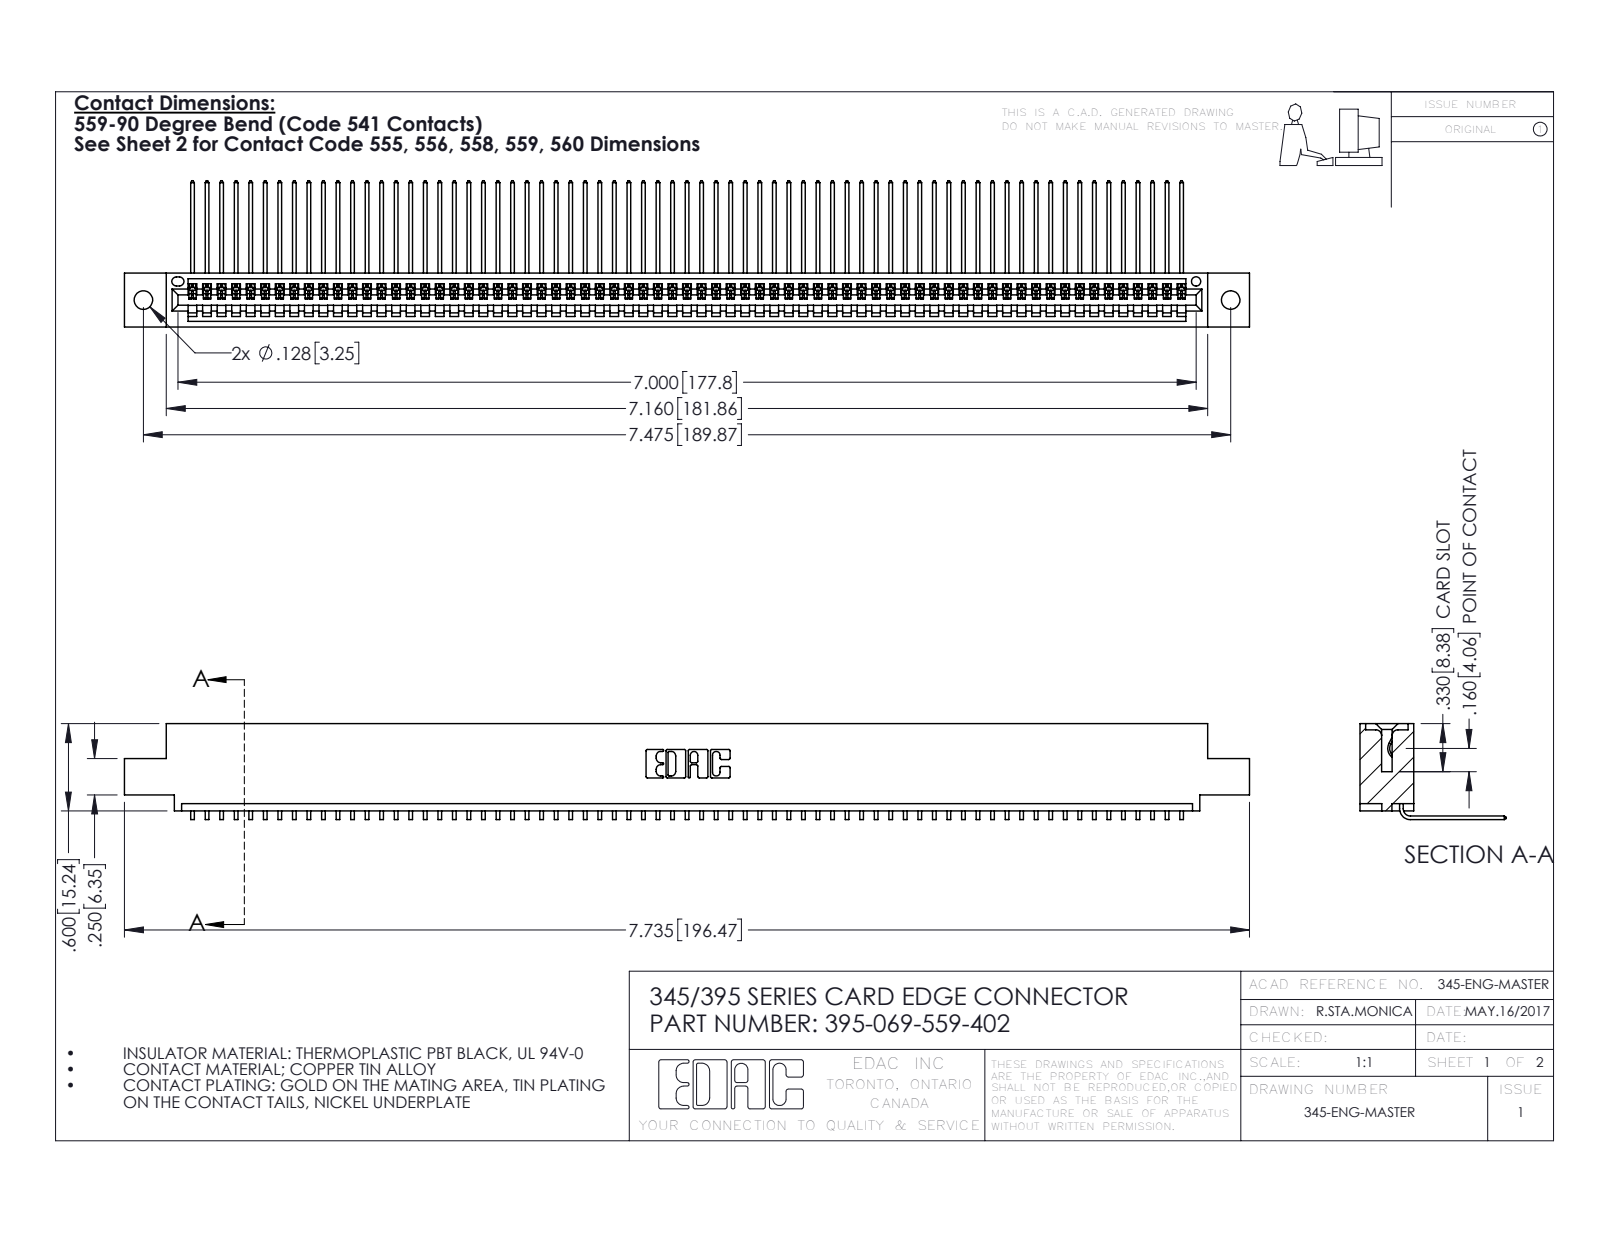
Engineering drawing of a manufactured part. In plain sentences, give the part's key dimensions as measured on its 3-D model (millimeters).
The part is named "345-292-001_558 559 Tail - 1; 345 Part_0.110 Offset - 0.128 Dia; 395-069-559-402". Its 3-D file was written by "SolidWorks 2016 (CONFIG_CONTROL_DESIGN)". It is 70 solids with 4270 faces: 2982 planar, 1288 cylindrical and 0 other. Overall it measures 196.5 by 25.5 by 16.7 millimeters. Its volume is 19 010 cubic millimeters and its surface area 26 780 square millimeters. Round holes: 2 of diameter 3.3, 1 of diameter 1.6. Partial cylindrical surfaces (rounded edges, fillets, slot ends): 138 of radius 0.2, 22 of radius 0.3, 6 of radius 0.2, 6 of radius 0.8, 3 of radius 0.7, 2 of radius 0.8, 2 of radius 1, 1 of radius 0.4. The main face-to-face distances are 1.8, 7.6, 9.4, 5.1, 2.5, 6.9, 0.6, 5.7, 3.8, 1.8. The hole center spacings are 6.9, 183.9, 189.9.
